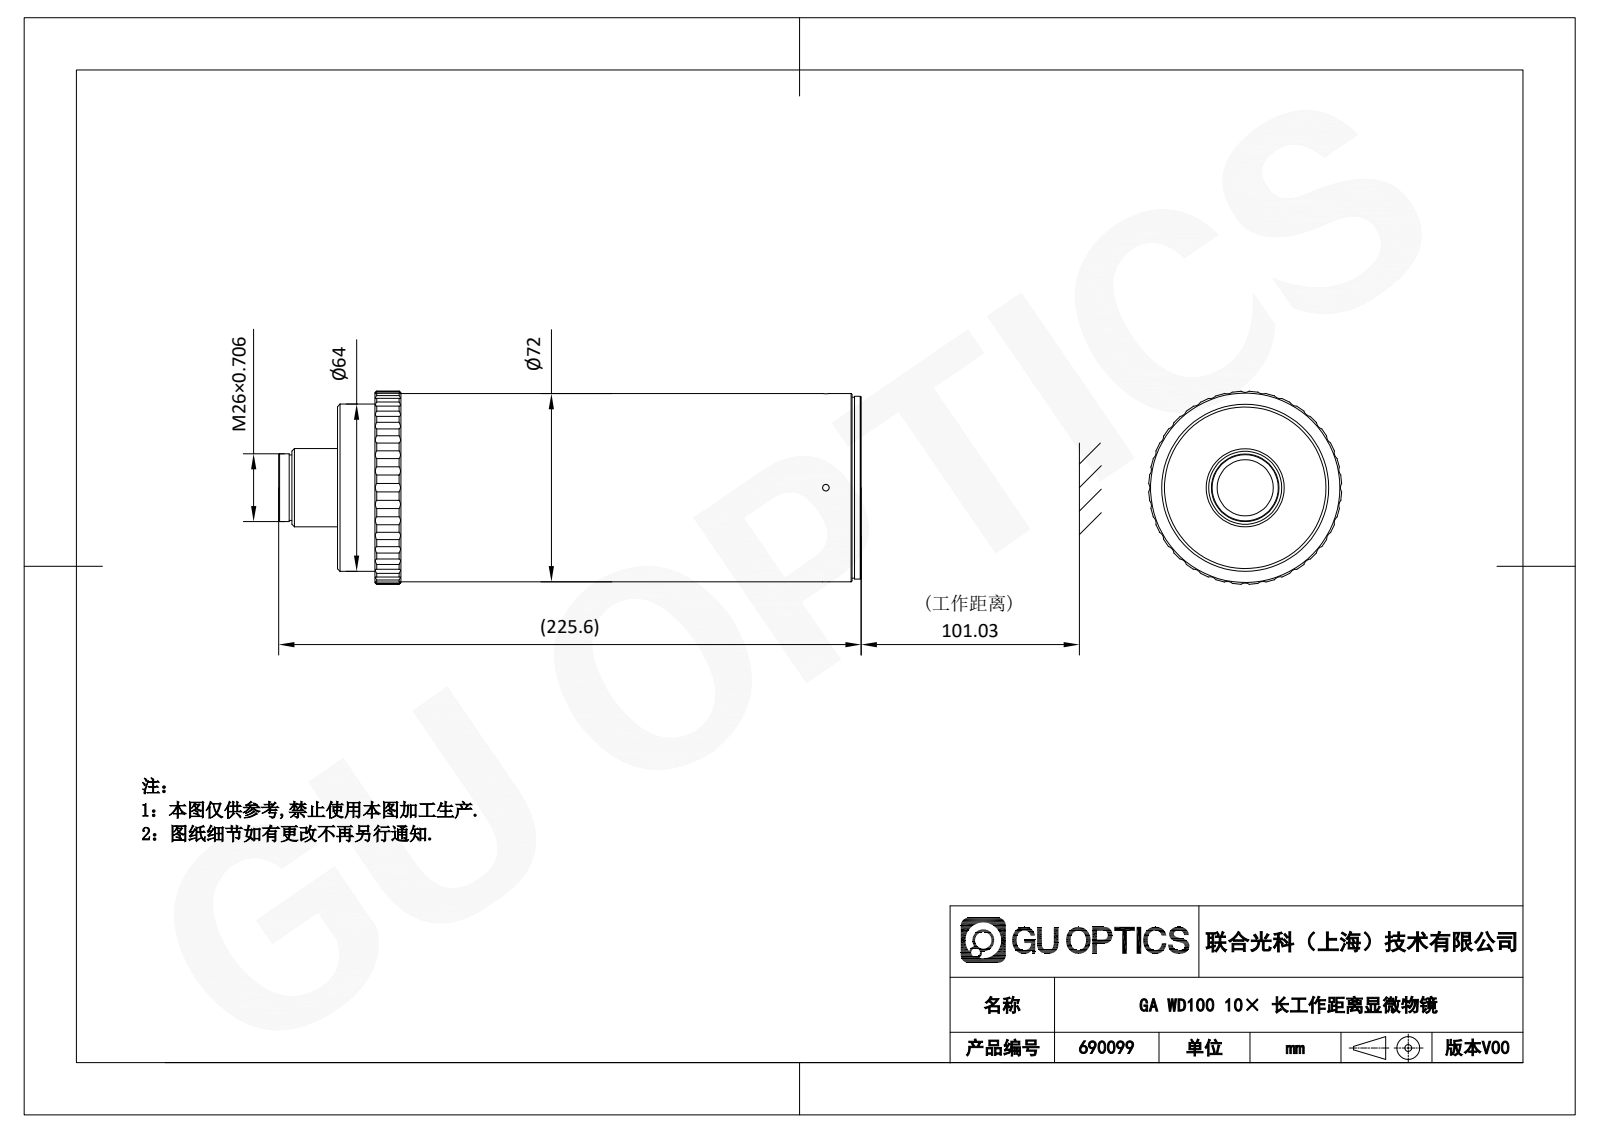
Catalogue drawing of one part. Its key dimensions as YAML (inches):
part_name: "690099"
step_written_by: "SolidWorks 2020 (CONFIG_CONTROL_DESIGN)"
units: inches
bodies: {solids: 1, faces: 501, planar: 120, cylindrical: 141, other: 240}
overall_size: [8.78, 2.911, 2.911]
volume: 10.25
surface_area: 161.2
round_holes:
  - {diameter: 0.098, count: 2}
  - {diameter: 0.689, count: 1}
  - {diameter: 0.787, count: 1}
  - {diameter: 0.846, count: 1}
  - {diameter: 0.872, count: 1}
  - {diameter: 0.945, count: 1}
  - {diameter: 2.244, count: 1}
  - {diameter: 2.48, count: 1}
  - {diameter: 2.618, count: 1}
round_bosses_or_shafts:
  - {diameter: 2.835, count: 1}
  - {diameter: 2.756, count: 1}
  - {diameter: 2.724, count: 1}
  - {diameter: 2.52, count: 1}
  - {diameter: 1.181, count: 1}
  - {diameter: 1.024, count: 1}
  - {diameter: 0.984, count: 1}
partial_cylinders:
  - {radius: 0.118, count: 36}
  - {radius: 1.418, count: 1}
  - {radius: 1.457, count: 1}
face_to_face_distances: [0.079, 7.815, 7.736, 7.685, 7.606, 0.13, 0.433, 0.563, 7.252, 7.173]
